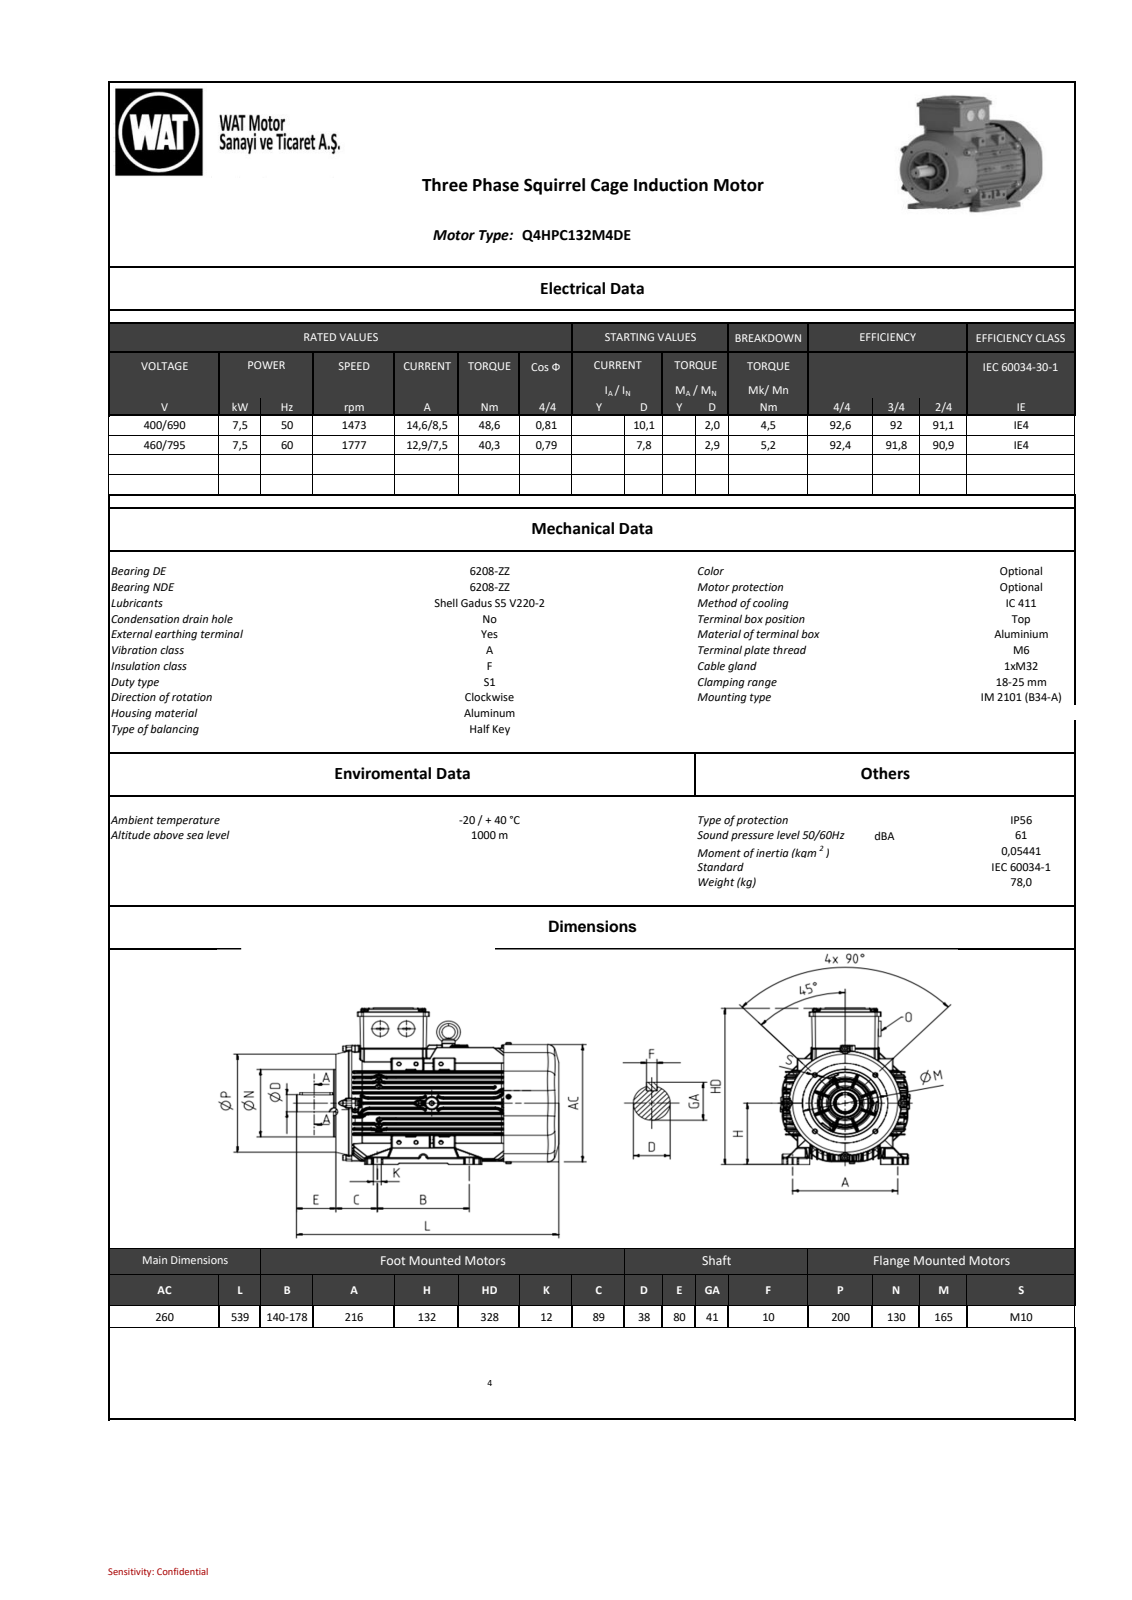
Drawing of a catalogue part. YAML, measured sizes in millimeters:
part_name: "260005841F74ycim"
step_written_by: "SIEMENS PLM Software NX 11.0 (AUTOMOTIVE_DESIGN)"
units: millimeters
bodies: {solids: 0, faces: 15861, planar: 3346, cylindrical: 5103, other: 7412}
overall_size: [538.95, 322.22, 267.74]
round_holes:
  - {diameter: 5.5, count: 8}
  - {diameter: 4, count: 6}
  - {diameter: 6.65, count: 4}
  - {diameter: 8.5, count: 4}
  - {diameter: 4.2, count: 2}
  - {diameter: 8.03, count: 2}
  - {diameter: 8.47, count: 2}
  - {diameter: 8.48, count: 2}
  - {diameter: 15, count: 2}
  - {diameter: 28, count: 2}
  - {diameter: 30.4, count: 2}
  - {diameter: 5.6, count: 1}
round_bosses_or_shafts:
  - {diameter: 8, count: 11}
  - {diameter: 4.2, count: 5}
  - {diameter: 20, count: 4}
  - {diameter: 13, count: 4}
  - {diameter: 38, count: 3}
  - {diameter: 32, count: 2}
  - {diameter: 8.5, count: 2}
  - {diameter: 230.5, count: 1}
partial_cylinders:
  - {radius: 0.8, count: 1497}
  - {radius: 1, count: 1477}
  - {radius: 0.1, count: 122}
  - {radius: 2, count: 110}
  - {radius: 0.5, count: 106}
  - {radius: 1.5, count: 41}
  - {radius: 3, count: 38}
  - {radius: 0.2, count: 21}
face_to_face_distances: [10.42, 1.5, 10.56, 3, 10.28, 20.84, 125.58, 115.18, 104.9, 94.46]
hole_center_spacings: [97.42, 170.45, 62.23, 88, 12.73, 74.95, 106, 120.5]
